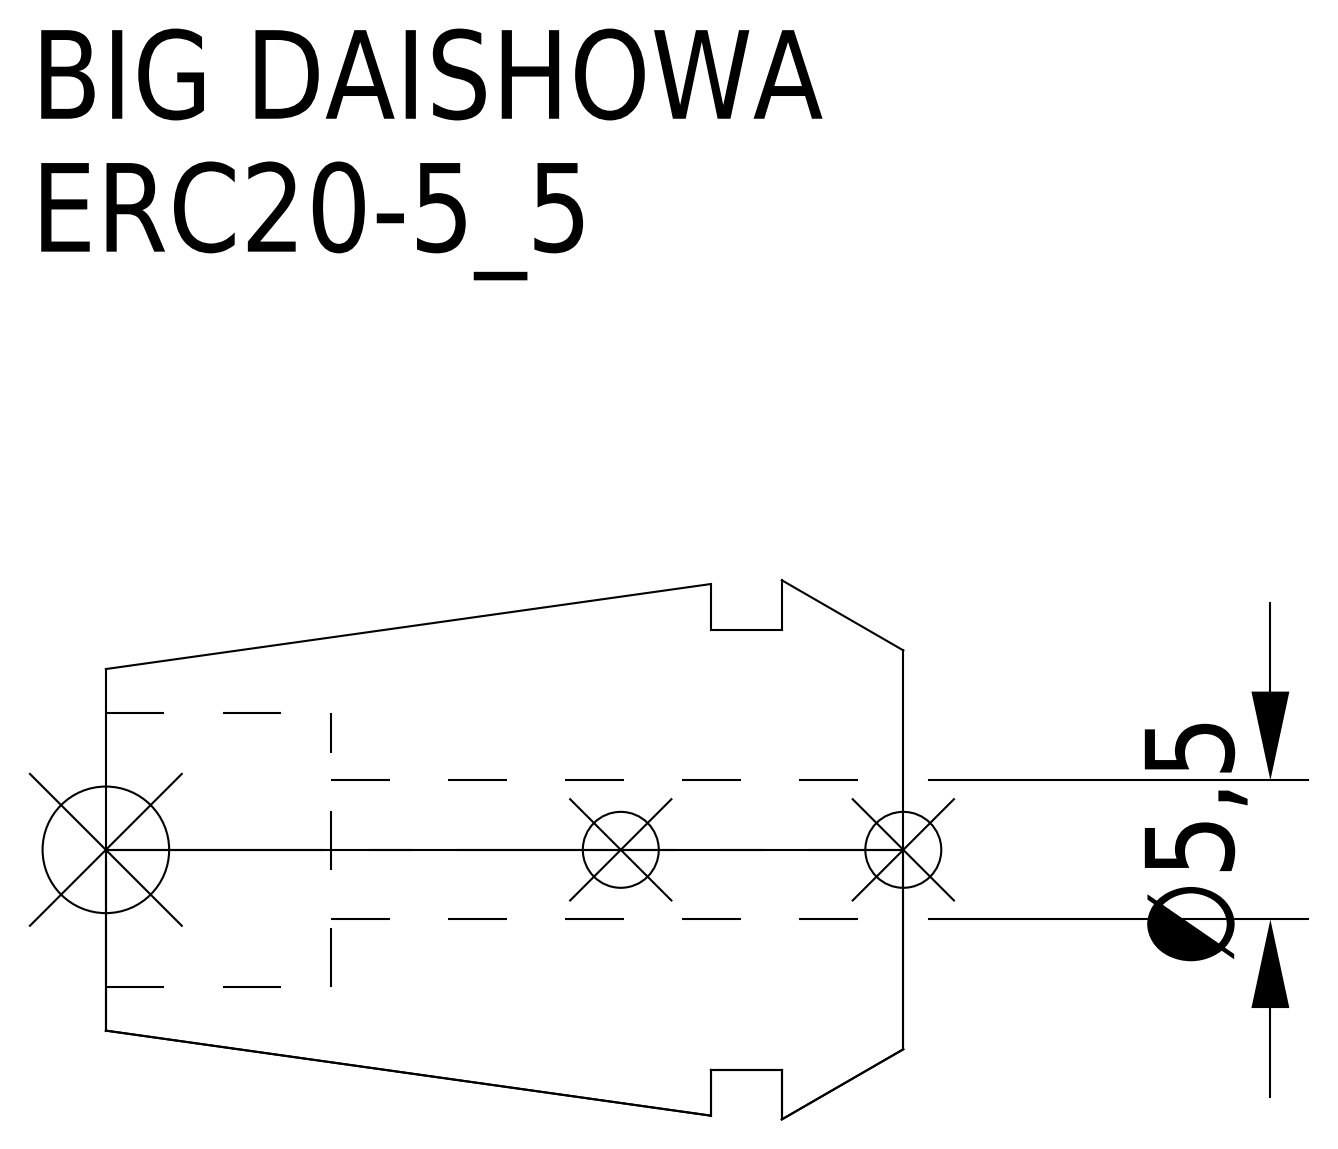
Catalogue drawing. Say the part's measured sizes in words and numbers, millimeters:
The part is named "ERC20-5_5". Its 3-D file was written by "CREO PARAMETRIC BY PTC INC, 2016380 (AUTOMOTIVE_DESIGN)". It is 1 solid with 15 faces: 5 planar, 6 cylindrical and 4 other. Overall it measures 31.5 by 21.3 by 21.3 millimeters. Its volume is 6 529 cubic millimeters and its surface area 3 041 square millimeters. Round holes: 1 of diameter 5.5, 1 of diameter 10.8. Round bosses or shafts: 1 of diameter 17.4. The main face-to-face distances are 4.8, 7.6, 2.8, 31.5, 26.7, 23.9, 22.59, 17.79, 14.99, 8.91.
